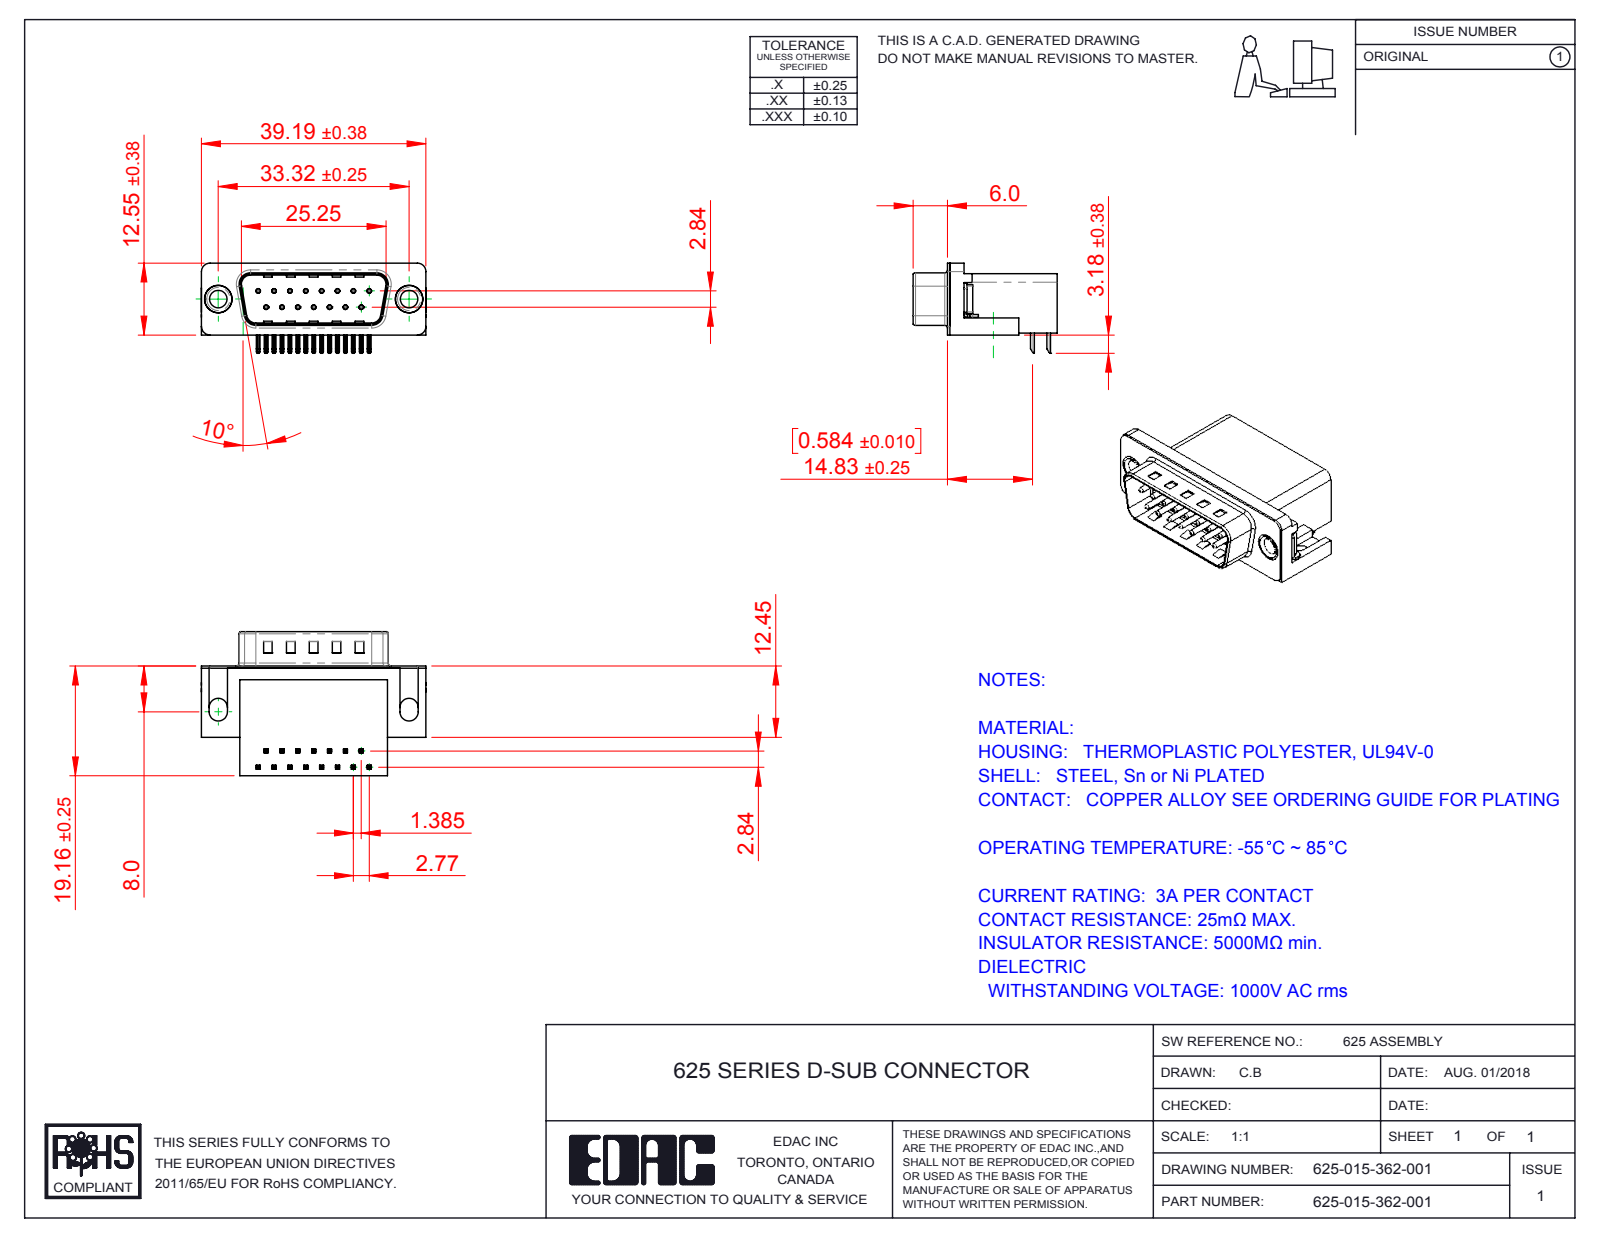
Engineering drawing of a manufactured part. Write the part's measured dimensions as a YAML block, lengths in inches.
part_name: "625 Contact Bottom; 625 Thru Hole Rivet; 625-015-362-001; 625 Shell_15 Socket (+3 more)"
step_written_by: "SolidWorks 2016 (CONFIG_CONTROL_DESIGN)"
units: inches
bodies: {solids: 21, faces: 1437, planar: 895, cylindrical: 425, other: 117}
overall_size: [1.544, 0.991, 0.619]
volume: 0.379
surface_area: 9.714
round_holes:
  - {diameter: 0.014, count: 15}
  - {diameter: 0.031, count: 15}
  - {diameter: 0.12, count: 2}
  - {diameter: 0.157, count: 2}
  - {diameter: 0.189, count: 2}
  - {diameter: 0.197, count: 2}
round_bosses_or_shafts:
  - {diameter: 0.03, count: 15}
  - {diameter: 0.193, count: 2}
  - {diameter: 0.187, count: 2}
  - {diameter: 0.152, count: 2}
partial_cylinders:
  - {radius: 0.01, count: 68}
  - {radius: 0.005, count: 30}
  - {radius: 0.039, count: 16}
  - {radius: 0.02, count: 9}
  - {radius: 0.063, count: 8}
  - {radius: 0.059, count: 6}
  - {radius: 0.035, count: 4}
  - {radius: 0.079, count: 4}
face_to_face_distances: [0.016, 0.407, 0.739, 0.083, 0.754, 0.412, 0.067, 0.428, 0.345, 0.64]
hole_center_spacings: [0.124, 0.109, 0.218, 0.327, 0.436, 0.198, 0.198, 0.294]
